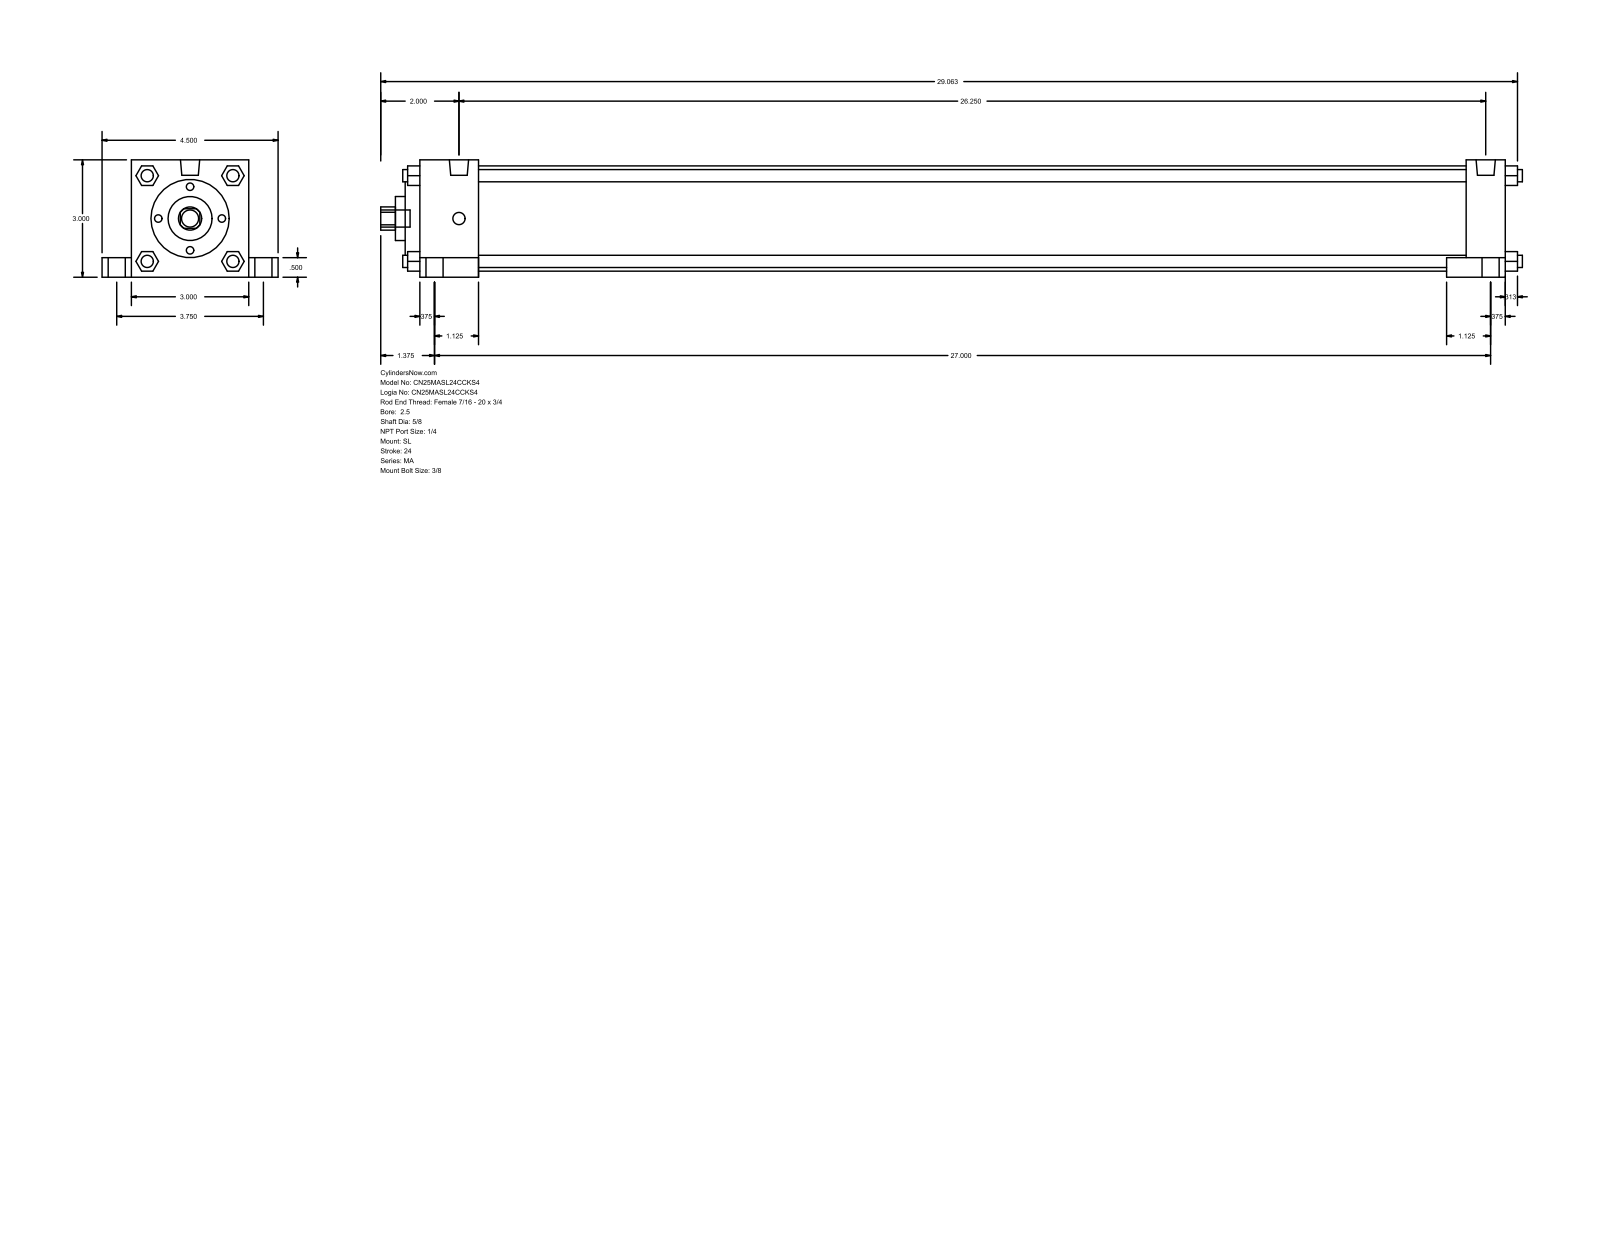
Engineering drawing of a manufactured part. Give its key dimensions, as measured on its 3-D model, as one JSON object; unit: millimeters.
{"part_name": "MA_SL__0250_0.625", "step_written_by": "GSSL Pune (CONFIG_CONTROL_DESIGN)", "units": "millimeters", "bodies": {"solids": 0, "faces": 150, "planar": 113, "cylindrical": 37, "other": 0}, "overall_size": [741.36, 114.3, 76.2], "round_holes": [[15.88, 1], [28.57, 1], [50.8, 1], [68.33, 1]], "round_bosses_or_shafts": [[7.94, 8], [11.11, 5], [17.46, 4], [12.49, 2]], "partial_cylinders_radius": [[7.54, 1]], "face_to_face_distances": [76.2, 704.85, 12.7, 641.35, 25.4, 38.1, 666.75, 679.45, 19.05, 63.5]}
